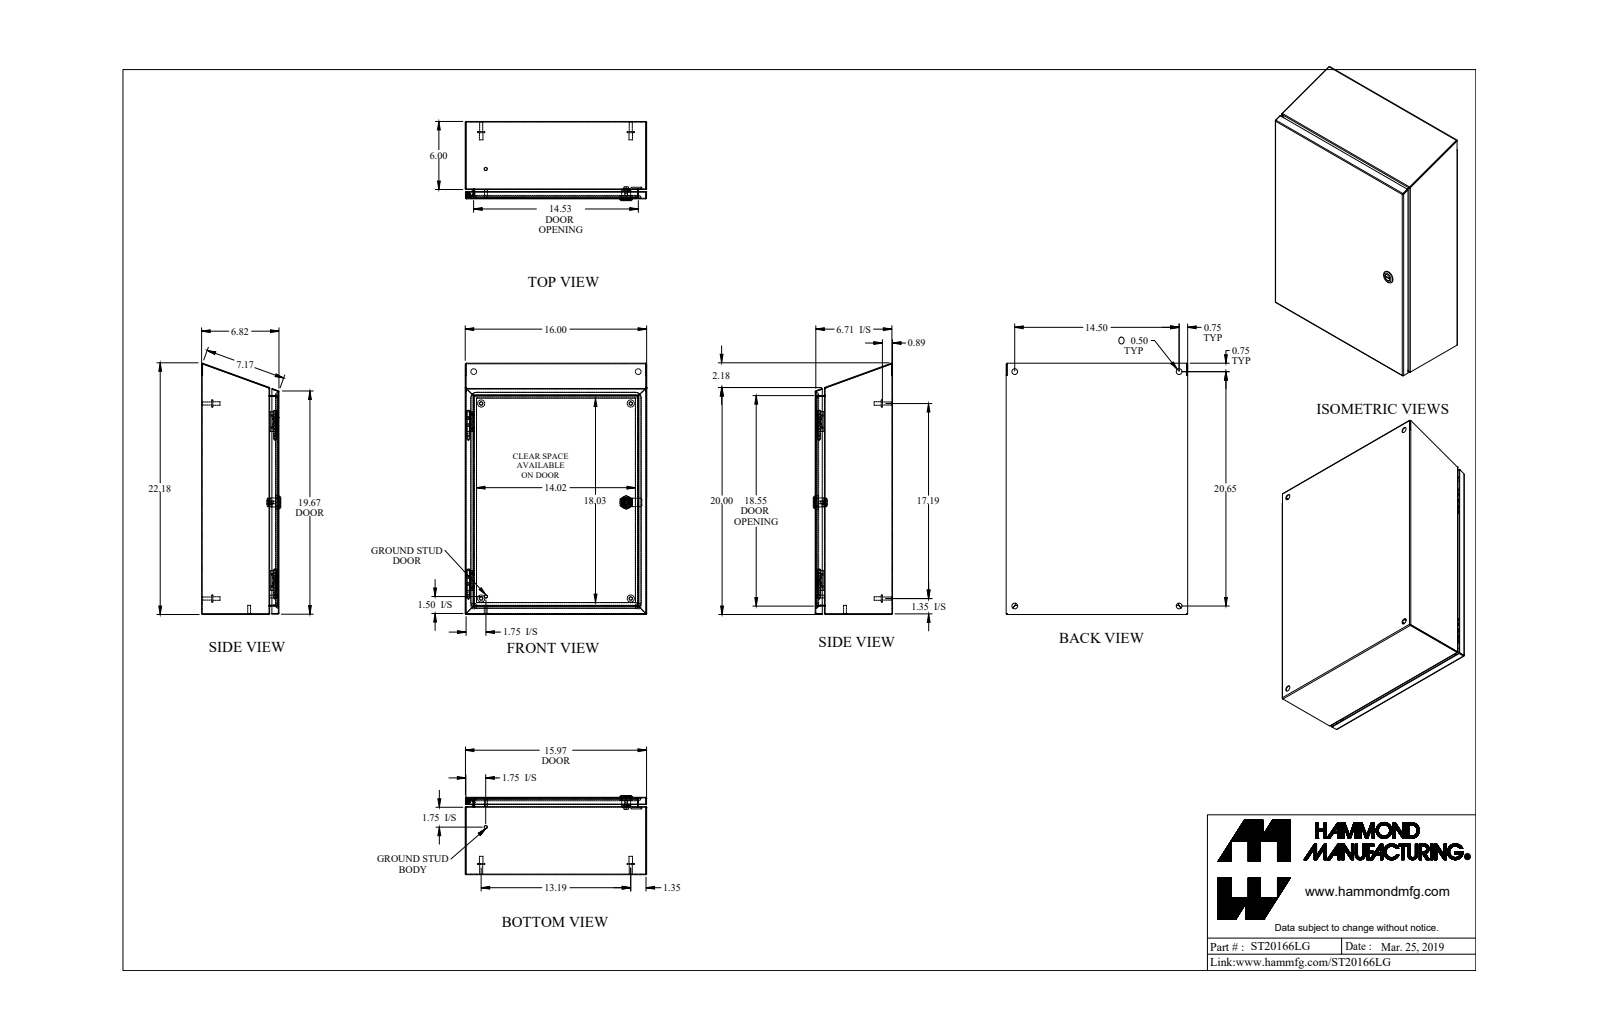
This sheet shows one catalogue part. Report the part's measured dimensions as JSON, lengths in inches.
{"part_name": "ST20166LG", "step_written_by": "SolidWorks 2018 (AUTOMOTIVE_DESIGN)", "units": "inches", "bodies": {"solids": 21, "faces": 632, "planar": 303, "cylindrical": 197, "other": 132}, "overall_size": [22.147, 16, 6.982], "volume_in3": 79.05, "surface_area_in2": 2682, "round_holes": [[0.5, 4], [0.172, 1], [0.232, 1], [0.24, 1], [0.242, 1], [0.625, 1], [0.785, 1]], "round_bosses_or_shafts": [[0.625, 4], [0.313, 4], [0.27, 4], [0.281, 2], [0.25, 2], [1.1, 1], [0.525, 1], [0.455, 1]], "partial_cylinders_radius": [[0.029, 21], [0.086, 21], [0.25, 11], [0.006, 4], [0.062, 4], [0.499, 4], [0.125, 2], [0.021, 1]], "face_to_face_distances": [0.057, 6.765, 6.708, 6.822, 15.943, 15.886, 16, 5.943, 0.822, 6], "hole_center_spacings": [14.5, 20.646, 25.23, 9.189, 11.567, 16.247, 17.702]}
